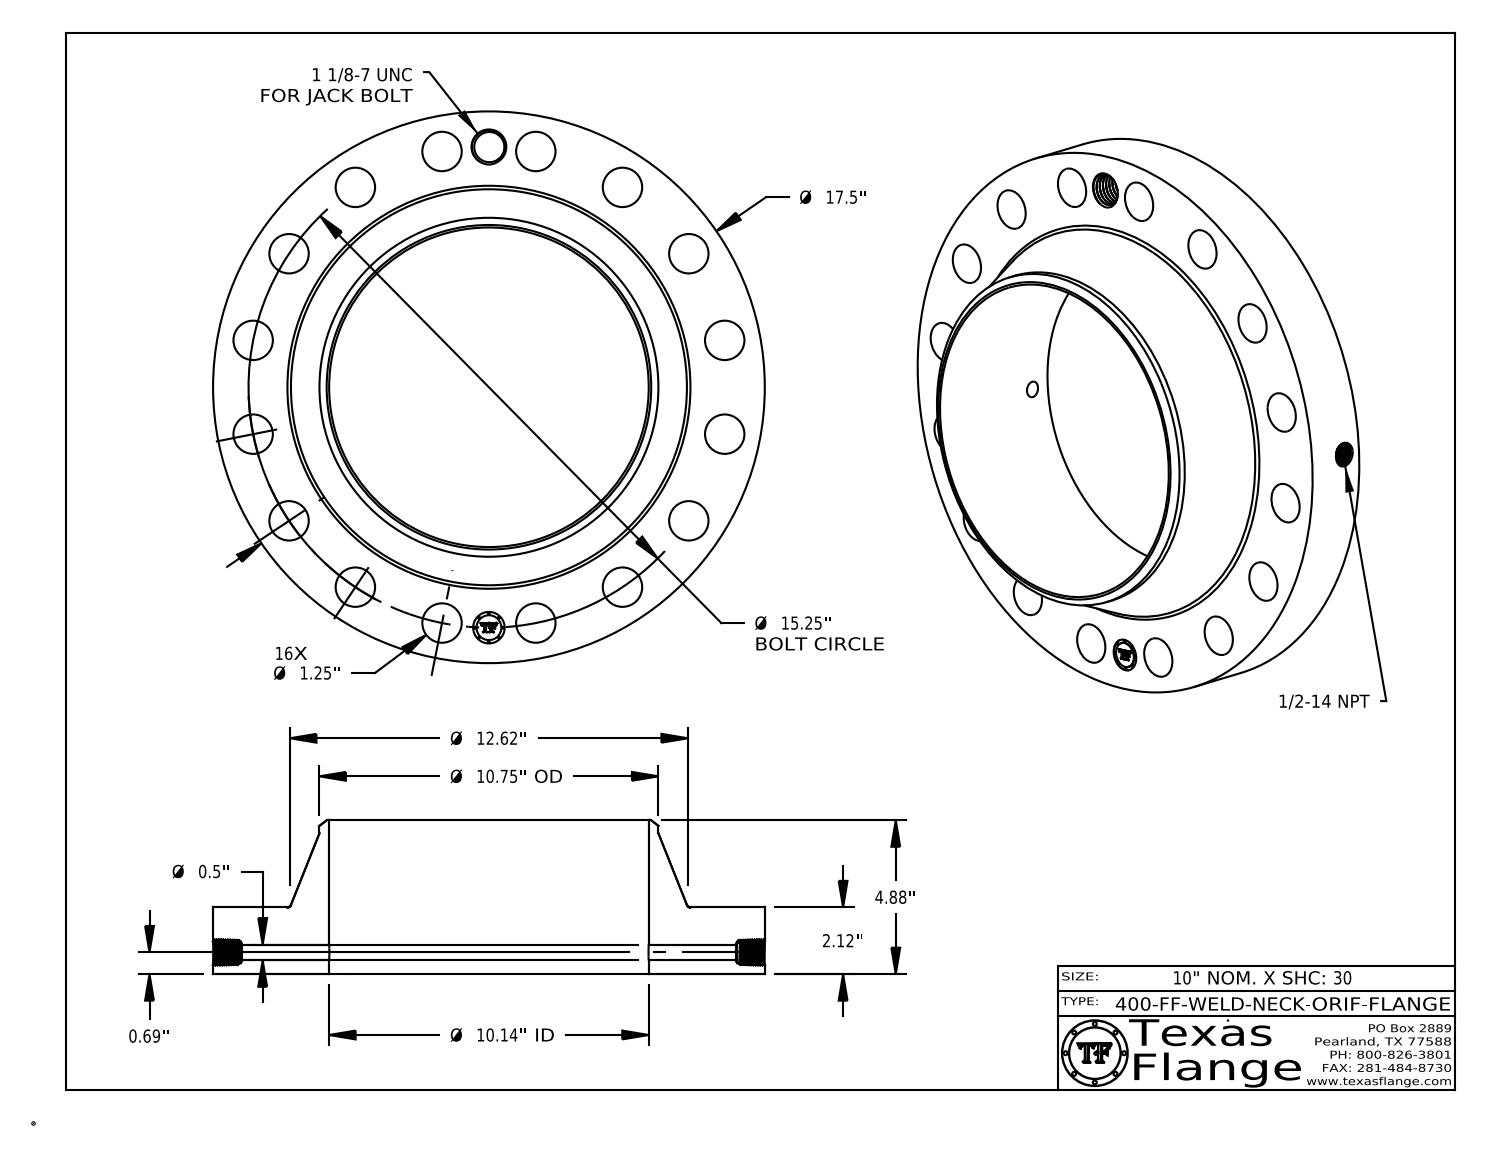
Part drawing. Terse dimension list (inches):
name: 400-FF-WELD-NECK
written by: CATIA V5 STEP AP214 (AUTOMOTIVE_DESIGN)
unit: in
bodies: 1 solid, 782 faces (368 planar, 107 cylindrical, 307 other)
size: 17.5 × 17.5 × 4.88
volume: 359.9 in³; area: 776.3 in²
holes: 16× ⌀1.25, 1× ⌀0.5, 1× ⌀0.672, 1× ⌀0.984, 1× ⌀1, 1× ⌀10.136
bosses: 8× ⌀0.061, 1× ⌀17.5, 1× ⌀10.75, 1× ⌀0.788
face distances: 2.12, 4.88, 2.76, 0.015, 2.105, 2.775, 0.298, 0.292, 0.054, 0.248
hole spacings: 5.836, 7.625, 10.783, 14.089, 14.957, 2.975, 2.975, 8.472
